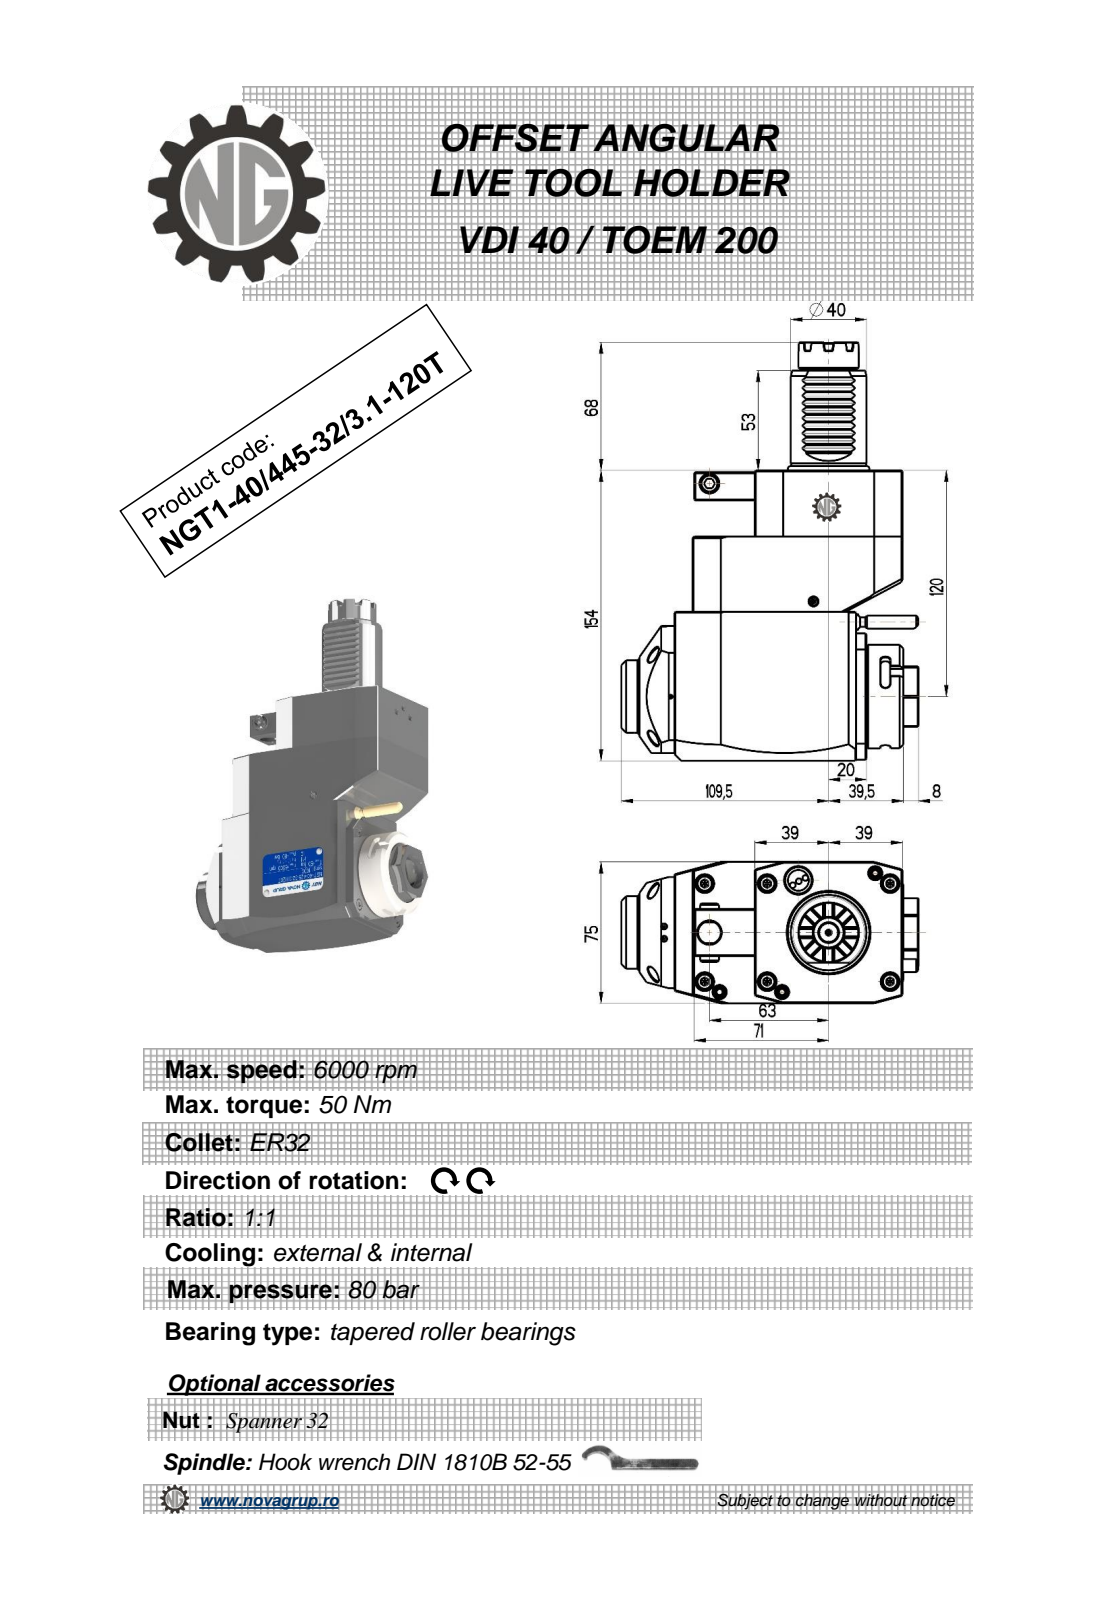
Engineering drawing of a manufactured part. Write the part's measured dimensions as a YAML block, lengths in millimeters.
part_name: "NGT1_40_445_32_3_1_120T"
step_written_by: "PRO/ENGINEER BY PARAMETRIC TECHNOLOGY CORPORATION, 2010280 (CONFIG_CONTROL_DESIGN)"
units: millimeters
bodies: {solids: 1, faces: 415, planar: 231, cylindrical: 74, other: 110}
overall_size: [222, 157, 75]
volume: 1283000
surface_area: 91333
round_holes:
  - {diameter: 2.5, count: 1}
  - {diameter: 3, count: 1}
  - {diameter: 8.5, count: 1}
  - {diameter: 9.5, count: 1}
  - {diameter: 12, count: 1}
  - {diameter: 23, count: 1}
round_bosses_or_shafts:
  - {diameter: 8.96, count: 2}
  - {diameter: 55, count: 1}
  - {diameter: 48, count: 1}
  - {diameter: 40, count: 1}
  - {diameter: 38.5, count: 1}
  - {diameter: 32, count: 1}
  - {diameter: 16.8, count: 1}
  - {diameter: 10, count: 1}
partial_cylinders:
  - {radius: 0.3, count: 10}
  - {radius: 2.5, count: 6}
  - {radius: 180, count: 2}
  - {radius: 0.5, count: 1}
  - {radius: 8.6, count: 1}
  - {radius: 24.5, count: 1}
  - {radius: 37.5, count: 1}
face_to_face_distances: [75, 154, 19, 59, 111, 35, 92, 119, 0.5, 33]
hole_center_spacings: [43.2, 75.07, 112.5]
